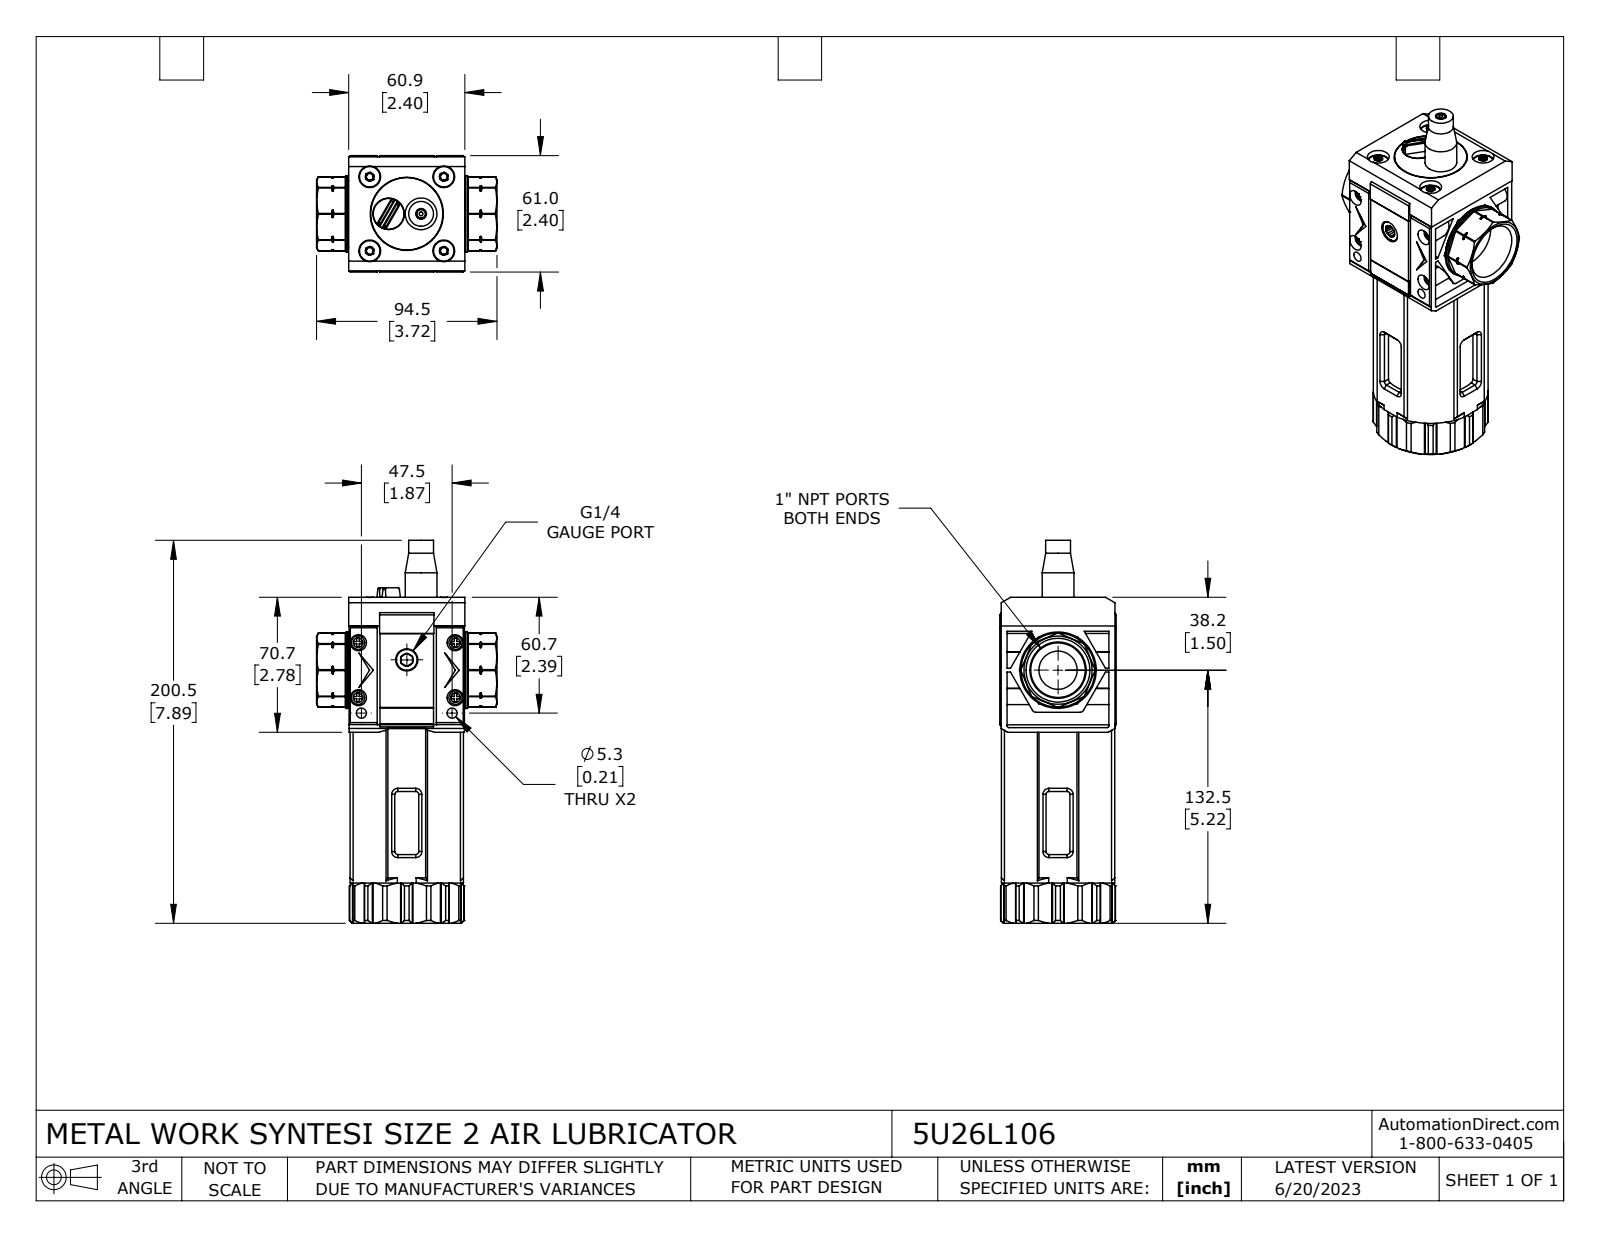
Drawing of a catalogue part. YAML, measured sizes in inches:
part_name: "5U26L106"
step_written_by: "SolidWorks 2021 (CONFIG_CONTROL_DESIGN)"
units: inches
bodies: {solids: 14, faces: 1230, planar: 551, cylindrical: 384, other: 295}
overall_size: [7.894, 3.72, 2.402]
volume: 24.08
surface_area: 200.8
round_holes:
  - {diameter: 0.128, count: 4}
  - {diameter: 0.165, count: 4}
  - {diameter: 0.331, count: 4}
  - {diameter: 0.449, count: 4}
  - {diameter: 0.209, count: 2}
  - {diameter: 0.22, count: 1}
  - {diameter: 0.457, count: 1}
  - {diameter: 0.65, count: 1}
  - {diameter: 0.787, count: 1}
  - {diameter: 1.25, count: 1}
  - {diameter: 1.508, count: 1}
  - {diameter: 1.929, count: 1}
round_bosses_or_shafts:
  - {diameter: 0.276, count: 4}
  - {diameter: 0.189, count: 4}
  - {diameter: 0.15, count: 4}
  - {diameter: 1.575, count: 1}
  - {diameter: 1.488, count: 1}
  - {diameter: 1.378, count: 1}
  - {diameter: 1.248, count: 1}
  - {diameter: 1.035, count: 1}
partial_cylinders:
  - {radius: 0.011, count: 28}
  - {radius: 0.02, count: 16}
  - {radius: 0.059, count: 8}
  - {radius: 0.069, count: 4}
  - {radius: 0.191, count: 4}
  - {radius: 0.008, count: 2}
  - {radius: 0.079, count: 2}
  - {radius: 0.242, count: 2}
face_to_face_distances: [2.39, 5.303, 3.205, 2.098, 1.13, 2.193, 2.402, 0.031, 3.11, 0.094]
hole_center_spacings: [1.08, 1.528, 0.325, 0.857, 0.896, 1.057, 1.134, 1.265]
